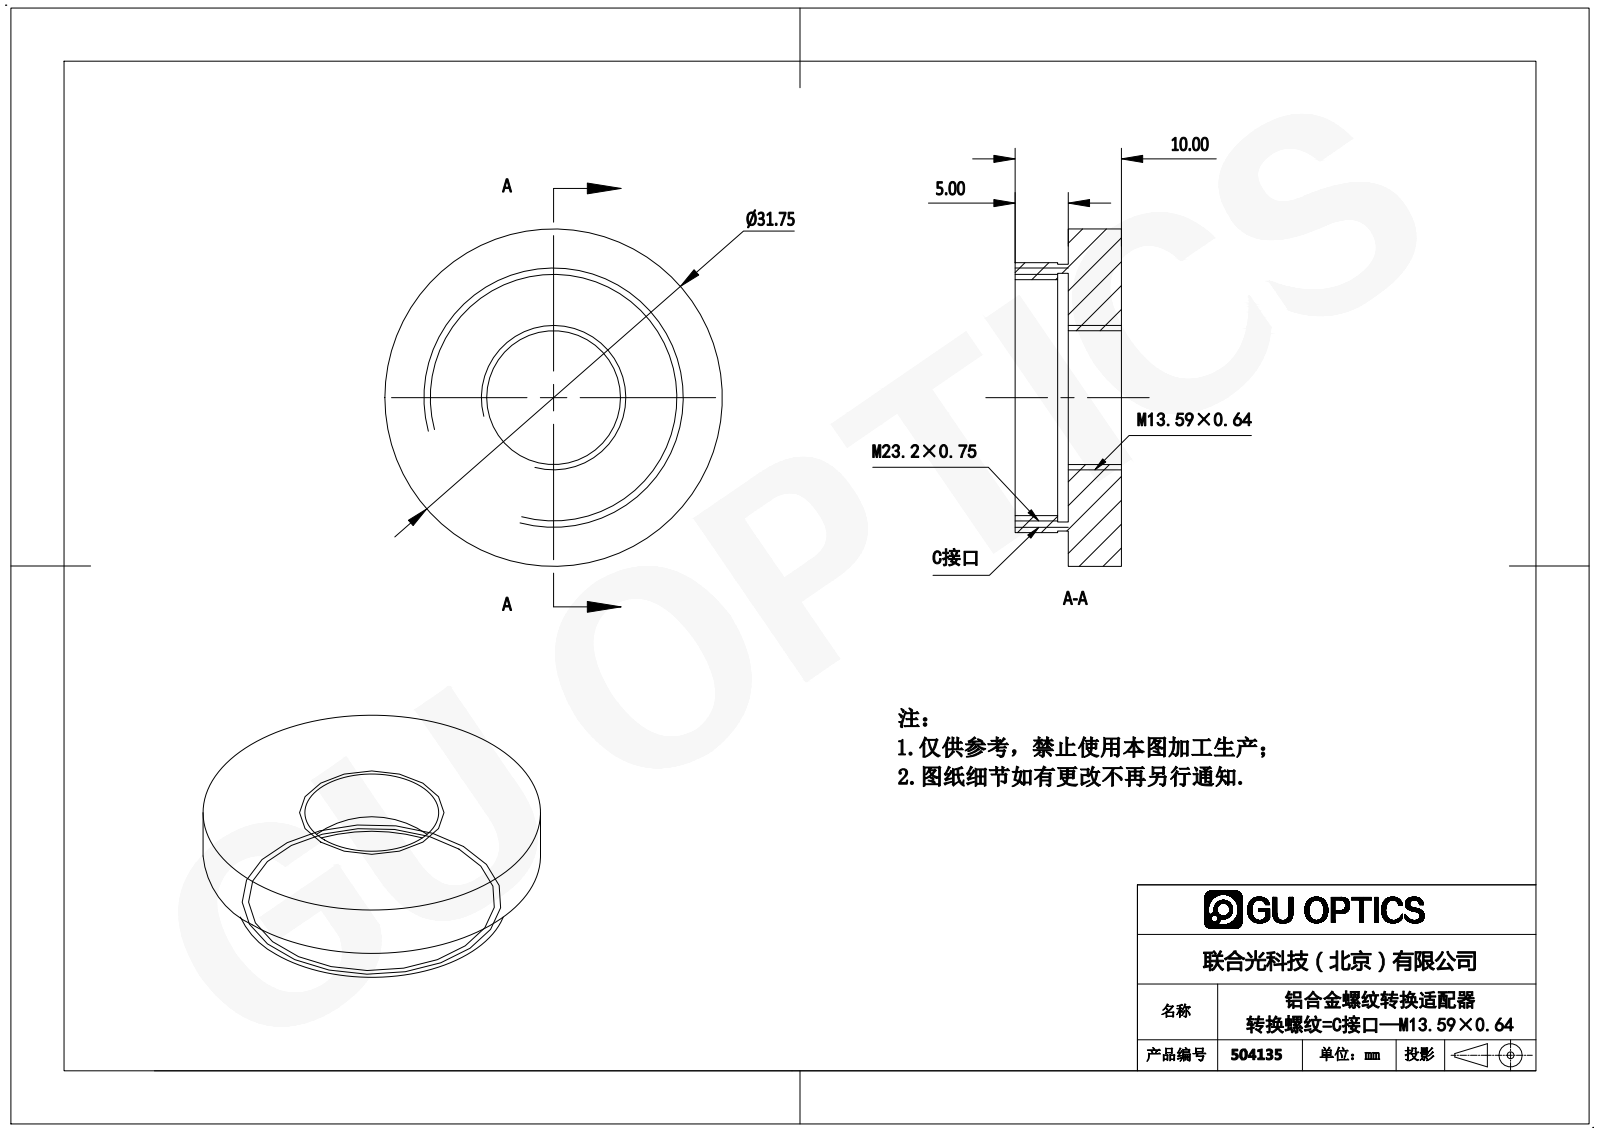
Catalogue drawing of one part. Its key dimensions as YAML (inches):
part_name: "504135"
step_written_by: "SolidWorks 2016 (AUTOMOTIVE_DESIGN)"
units: inches
bodies: {solids: 1, faces: 18, planar: 6, cylindrical: 12, other: 0}
overall_size: [1.25, 1.25, 0.394]
volume: 0.237
surface_area: 4.481
round_holes:
  - {diameter: 0.496, count: 1}
  - {diameter: 0.874, count: 1}
  - {diameter: 0.921, count: 1}
round_bosses_or_shafts:
  - {diameter: 1.25, count: 1}
  - {diameter: 1, count: 1}
  - {diameter: 0.988, count: 1}
face_to_face_distances: [0.197, 0.394, 0.157, 0.039, 0.236]
